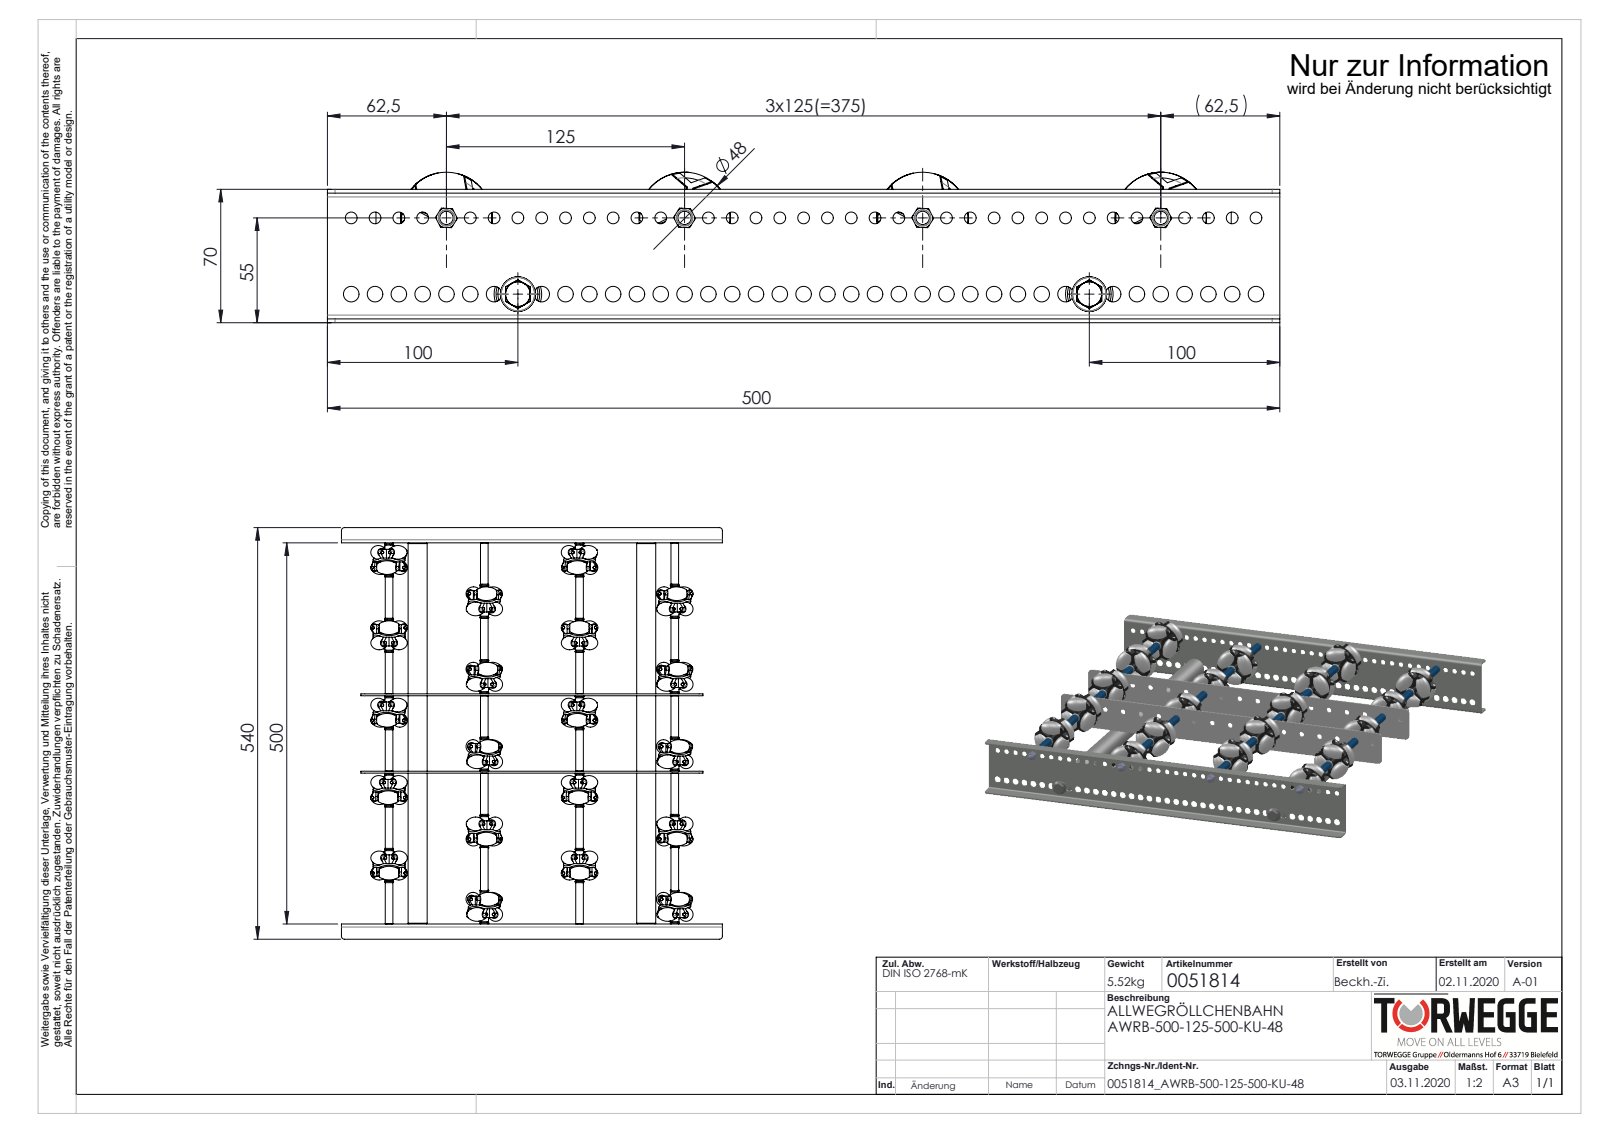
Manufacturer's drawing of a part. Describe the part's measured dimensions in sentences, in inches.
The part is named "0051814; S100994_Sperrzahnschraube_M08x16-8.8-A2K; 0019730_Tragrollenrohr-Ø10x1,75KU_KFG_0019730_L=54; 0019719_Gewindestange-M6_L=520 (+8 more)". Its 3-D file was written by "SolidWorks 2020 (AUTOMOTIVE_DESIGN)". It is 346 solids with 6388 faces: 2164 planar, 2568 cylindrical and 1656 other. Overall it measures 21.26 by 19.685 by 3.11 inches. Its volume is 86.41 cubic inches and its surface area 1 621 square inches. Round holes: 120 of diameter 0.146, 120 of diameter 0.165, 39 of diameter 0.244, 39 of diameter 0.323, 18 of diameter 0.256, 4 of diameter 0.194, 4 of diameter 0.331, 2 of diameter 0.268, 2 of diameter 0.827. Round bosses or shafts: 120 of diameter 0.157, 106 of diameter 0.146, 6 of diameter 0.315, 4 of diameter 1.654, 4 of diameter 0.433, 4 of diameter 0.394, 4 of diameter 0.276, 4 of diameter 0.236. Partial cylindrical surfaces (rounded edges, fillets, slot ends): 8 of radius 0.157, 4 of radius 0.079, 4 of radius 0.197, 4 of radius 0.927. The main face-to-face distances are 0.079, 19.764, 3.996, 0.098, 2.677, 19.685, 19.843, 0.581, 0.118, 3.898. The hole center spacings are 1.42, 1.419, 0.492, 0.984, 1.476, 1.969, 1.419, 2.461.
